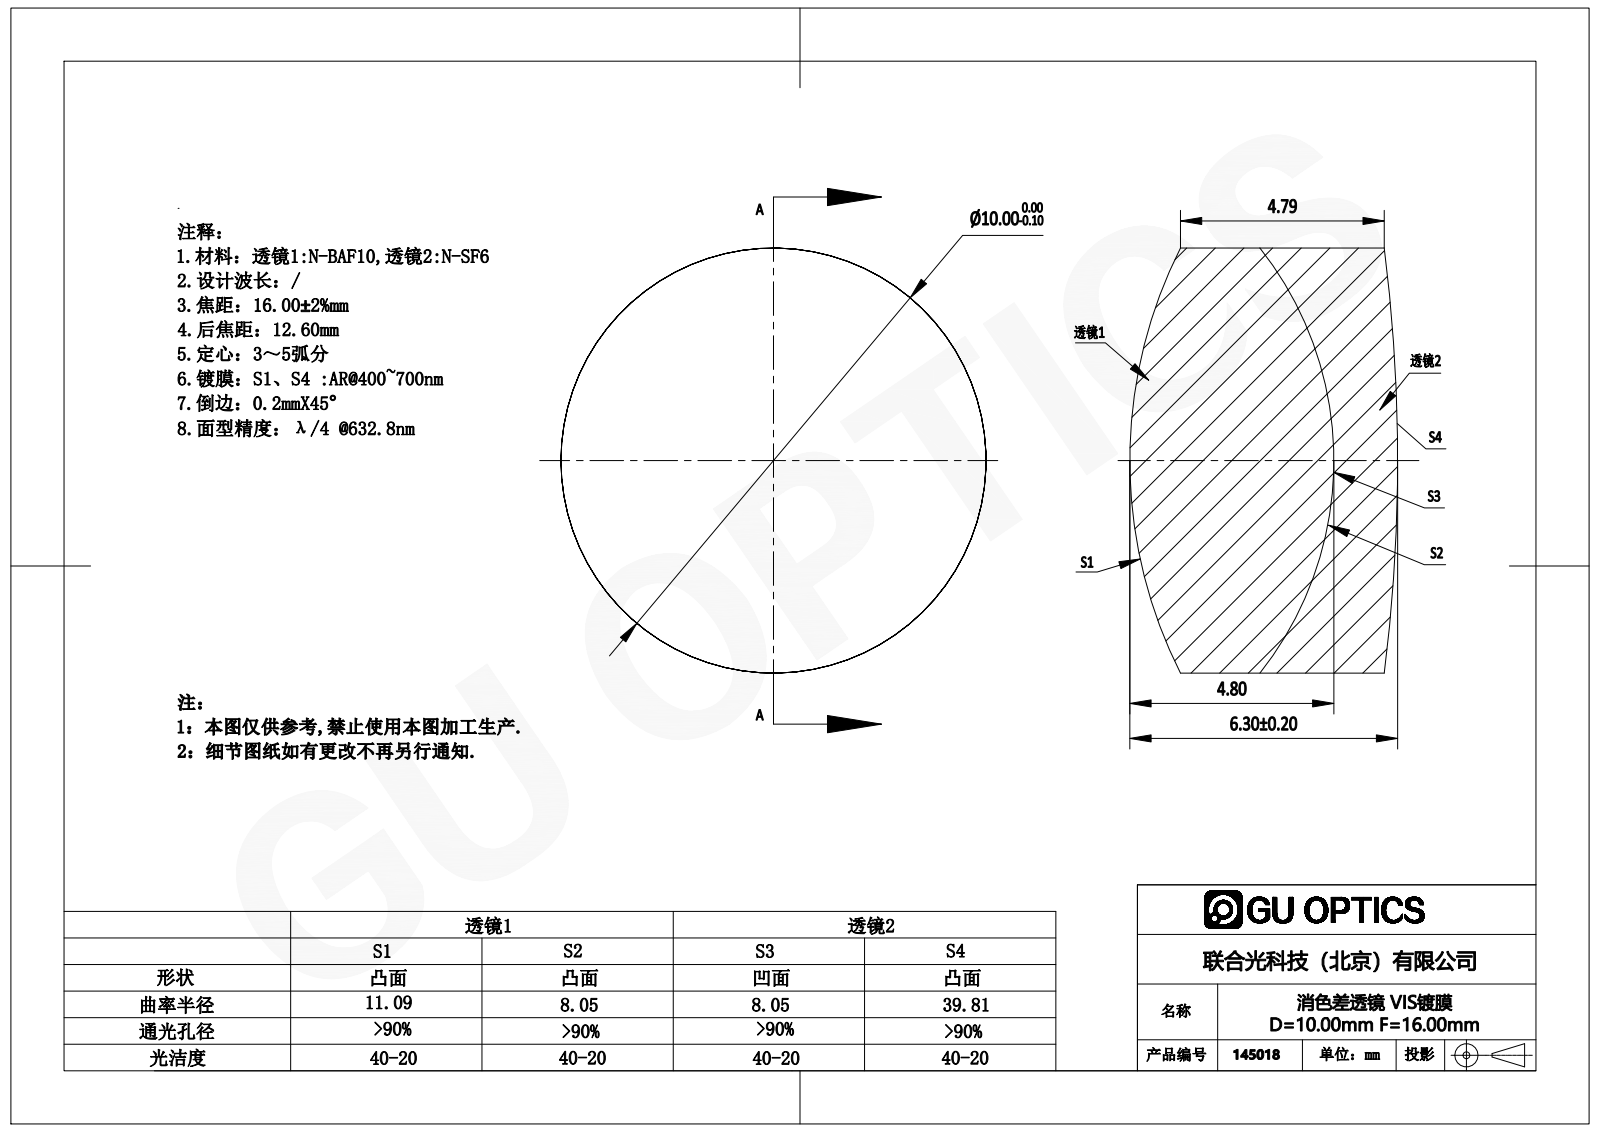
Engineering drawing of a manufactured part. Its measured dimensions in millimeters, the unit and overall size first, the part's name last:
Units: millimetres
Overall size (bounding box): 10 × 10 × 6.3
Round bosses / shafts (diameter × count): ⌀10 ×1
Volume: 437 mm³ · Surface area: 489 mm²
Bodies: 2 solids, 12 faces (0 planar, 4 cylindrical, 8 other)
Part name (STEP PRODUCT): 145018
STEP written by: SolidWorks 2016 (AUTOMOTIVE_DESIGN)
